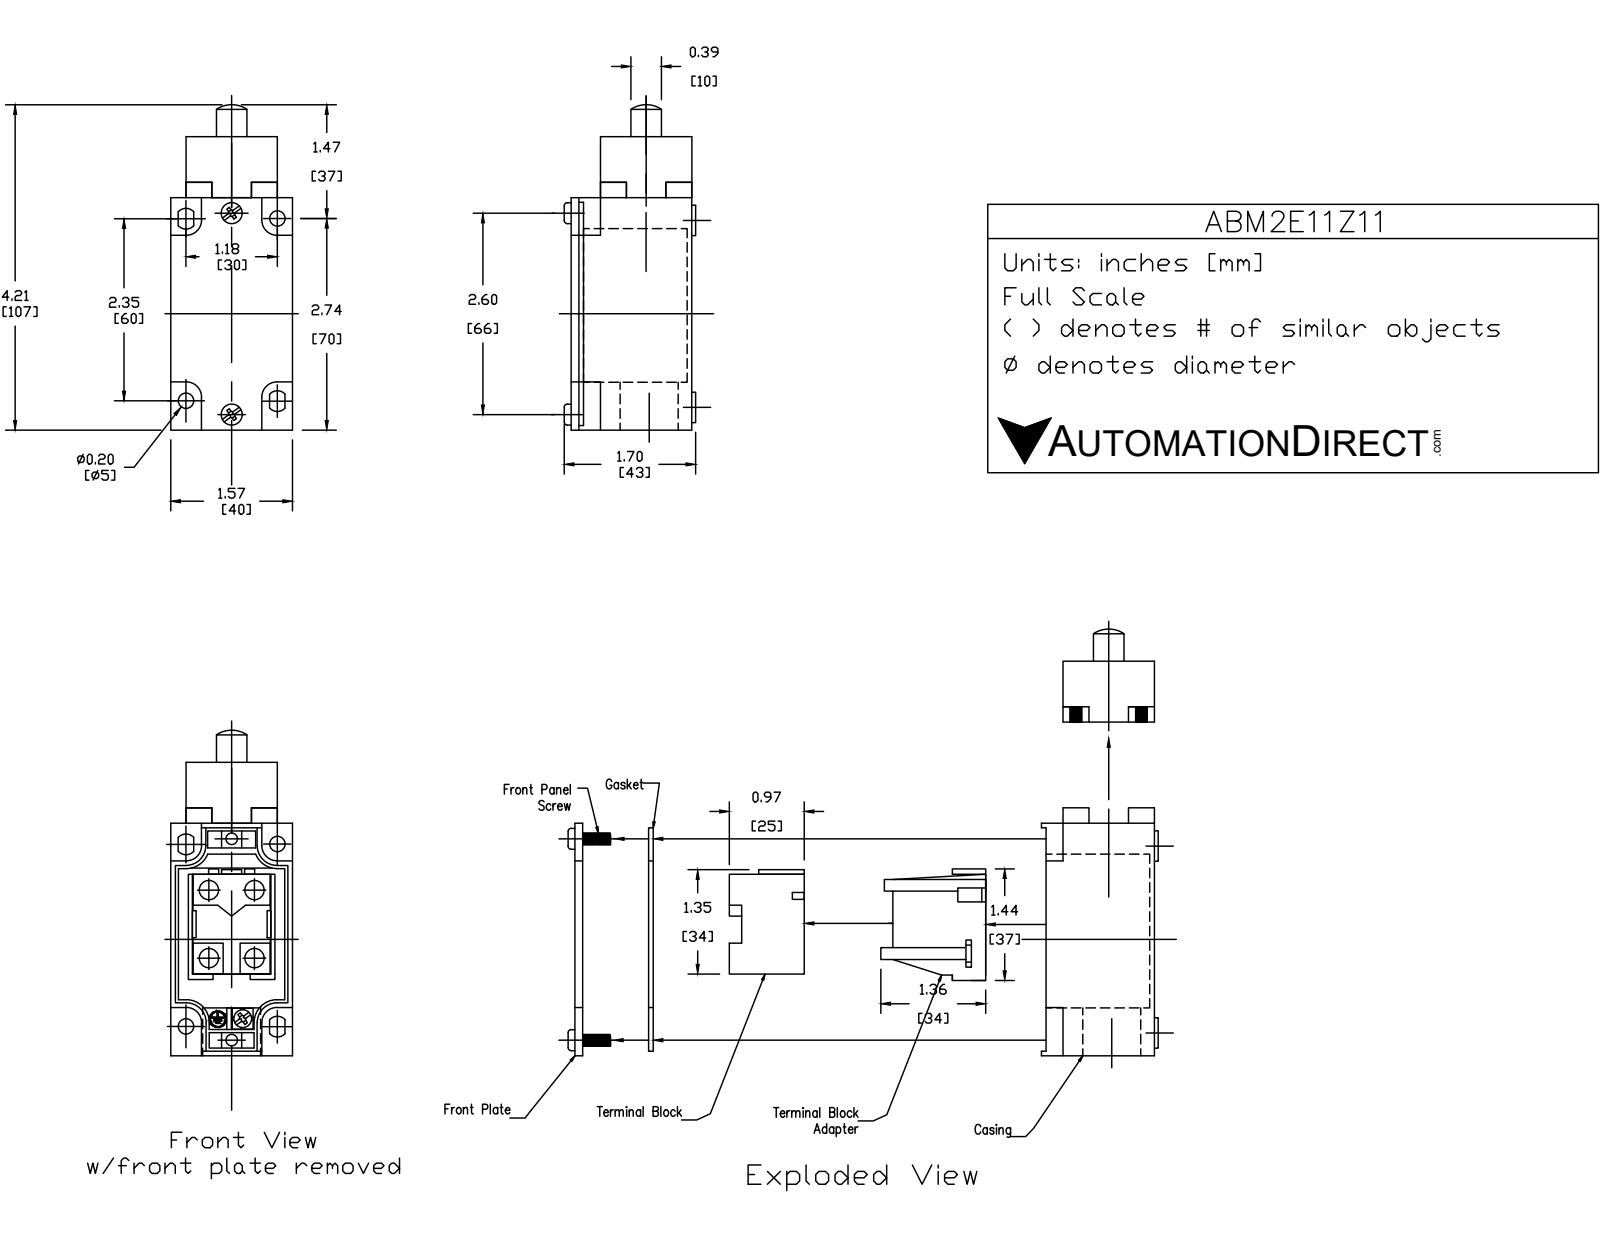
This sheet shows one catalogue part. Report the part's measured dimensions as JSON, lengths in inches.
{"part_name": "ABM2E11Z11", "step_written_by": "SolidWorks 2017 (AUTOMOTIVE_DESIGN)", "units": "inches", "bodies": {"solids": 3, "faces": 151, "planar": 68, "cylindrical": 66, "other": 17}, "overall_size": [4.196, 1.705, 1.575], "volume_in3": 7.787, "surface_area_in2": 37.63, "round_holes": [[0.205, 2], [0.394, 1], [0.669, 1], [0.748, 1]], "round_bosses_or_shafts": [[0.394, 4], [0.276, 2]], "partial_cylinders_radius": [[0.059, 16], [0.039, 4], [0.197, 4], [0.128, 2], [0.453, 1], [0.472, 1]], "face_to_face_distances": [1.575, 1.555, 1.181, 0.197, 1.378, 0.374, 3.012, 3.209, 0.591, 3.031], "hole_center_spacings": [0.039, 2.641]}
